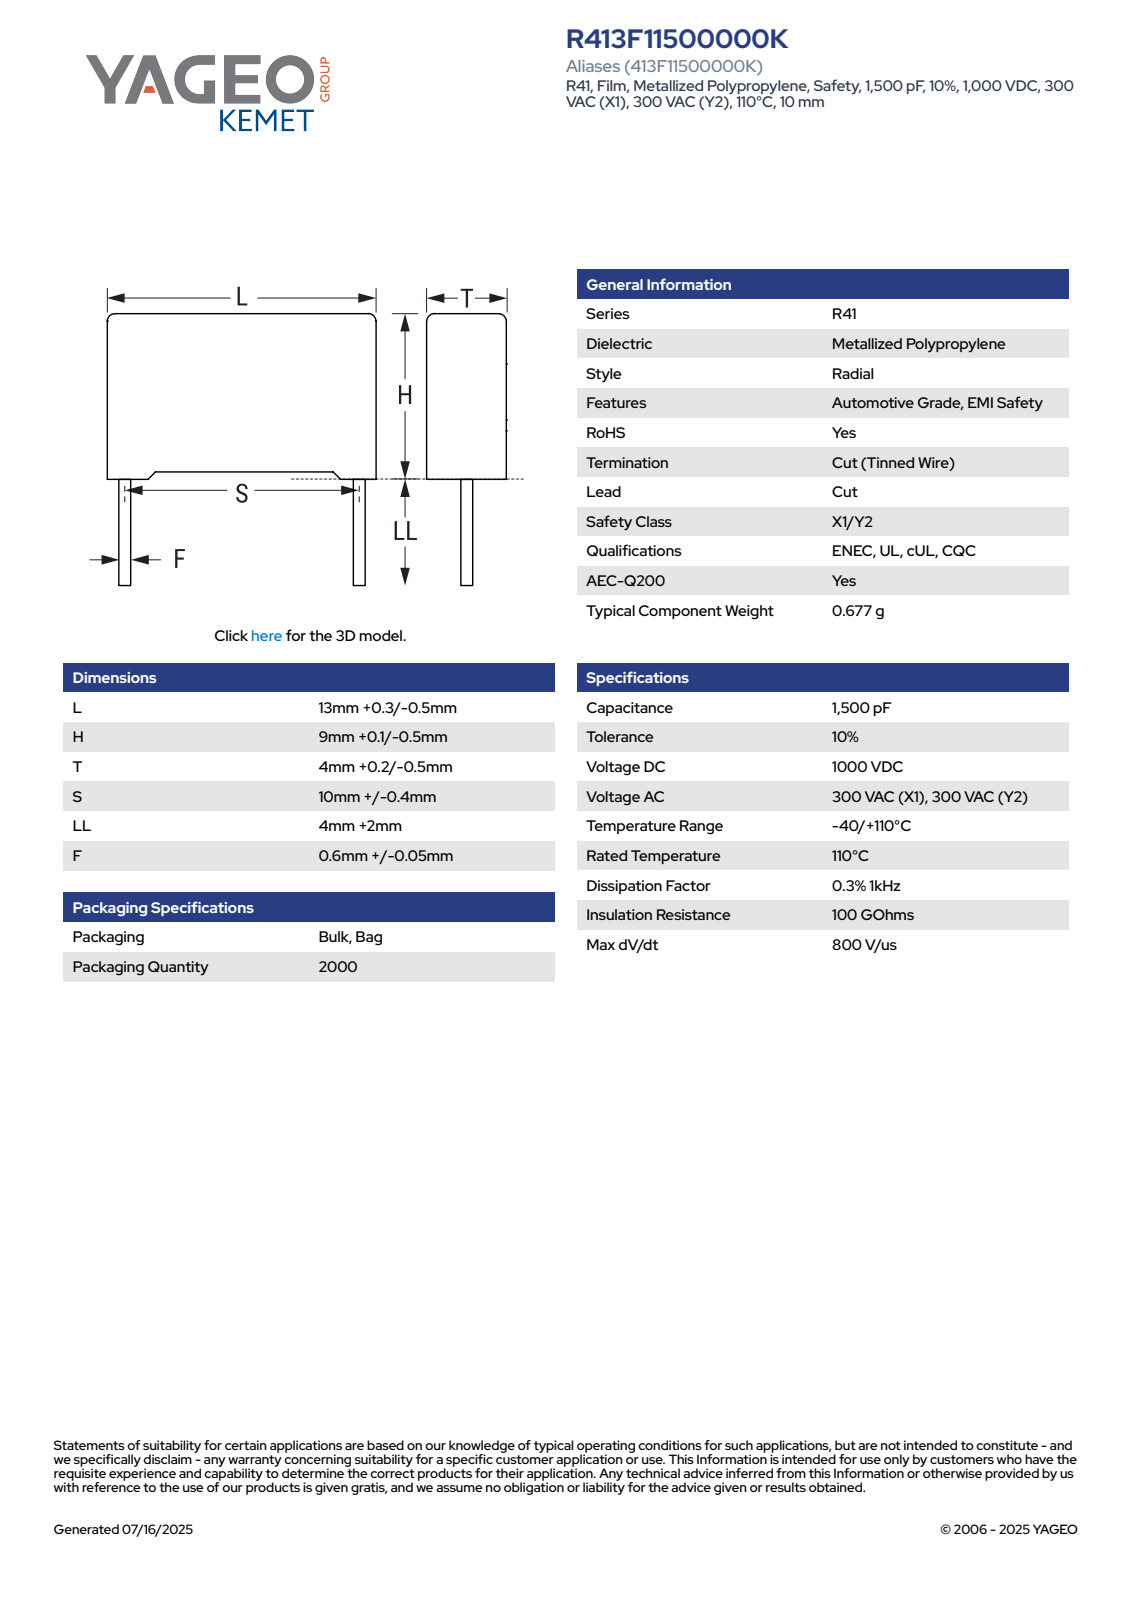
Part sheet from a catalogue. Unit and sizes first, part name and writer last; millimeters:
Units: millimetres
Overall size (bounding box): 15.1 × 13.3 × 4.21
Round bosses / shafts (diameter × count): ⌀0.65 ×2
Partial cylindrical surfaces — rounded edges, fillets, slot ends (radius × count): R0.5 ×4
Main face-to-face distances: 4.2, 8.35, 13.3, 0.44, 3.76, 0.75, 9.1, 3.32, 0.31, 8.79
Volume: 478 mm³ · Surface area: 479 mm²
Bodies: 4 solids, 85 faces (77 planar, 8 cylindrical, 0 other)
Part name (STEP PRODUCT): CFR_RB2_13X9X4_L13.3H9.1T4.2S10LL6F0.65
STEP written by: SolidWorks 2021 (AUTOMOTIVE_DESIGN)
